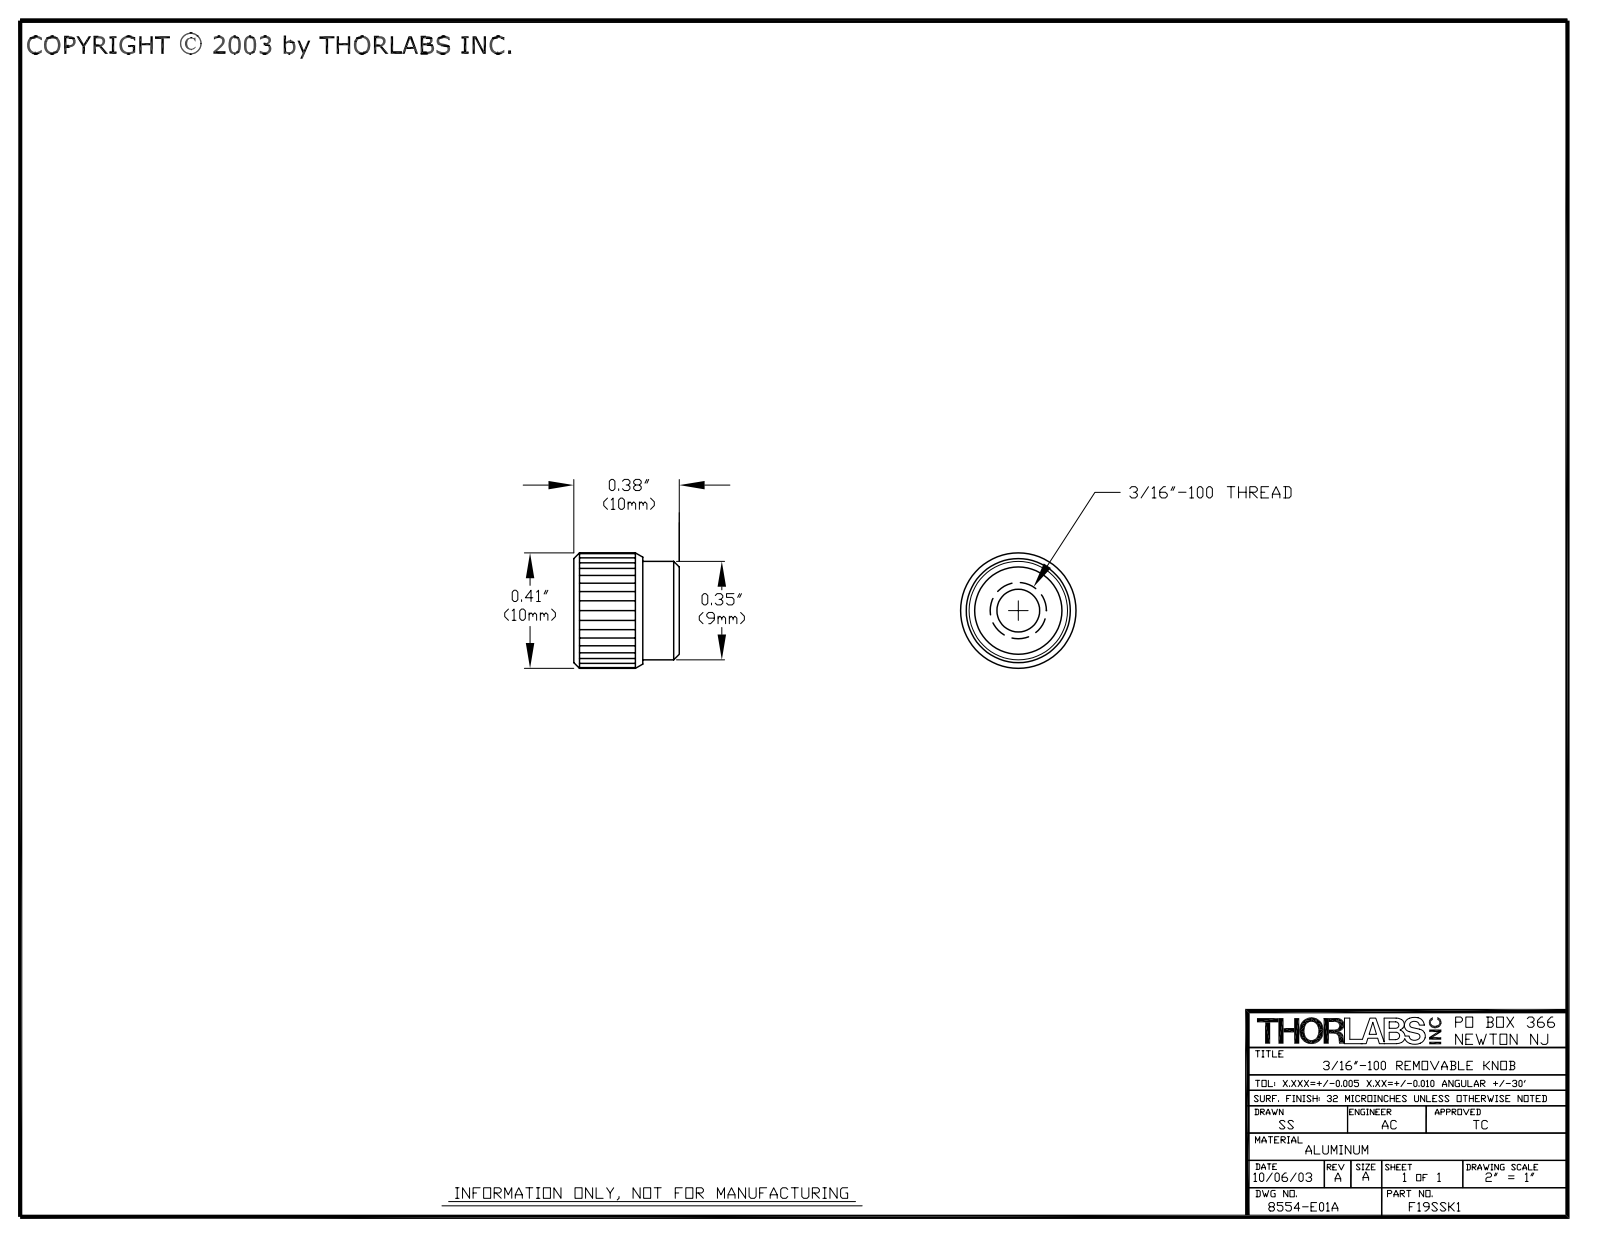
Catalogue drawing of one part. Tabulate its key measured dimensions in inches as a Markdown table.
| quantity | value |
| --- | --- |
| part name | 8554-E0W |
| STEP written by | SolidWorks 2011 (AUTOMOTIVE_DESIGN) |
| units | inches |
| bodies | 1 solid, 115 faces (7 planar, 100 cylindrical, 8 other) |
| overall size | 0.41 × 0.41 × 0.38 |
| volume | 0.036 in³ |
| surface area | 1.3 in² |
| round holes (diameter × count) | 0.13 × 1, 0.143 × 1, 0.187 × 1, 0.32 × 1 |
| round bosses / shafts (diameter × count) | 0.41 × 1, 0.34 × 1 |
| main face-to-face distances | 0.36, 0.38, 0.02, 0.13, 0.23, 0.25, 0.227, 0.097, 0.133, 0.153 |
